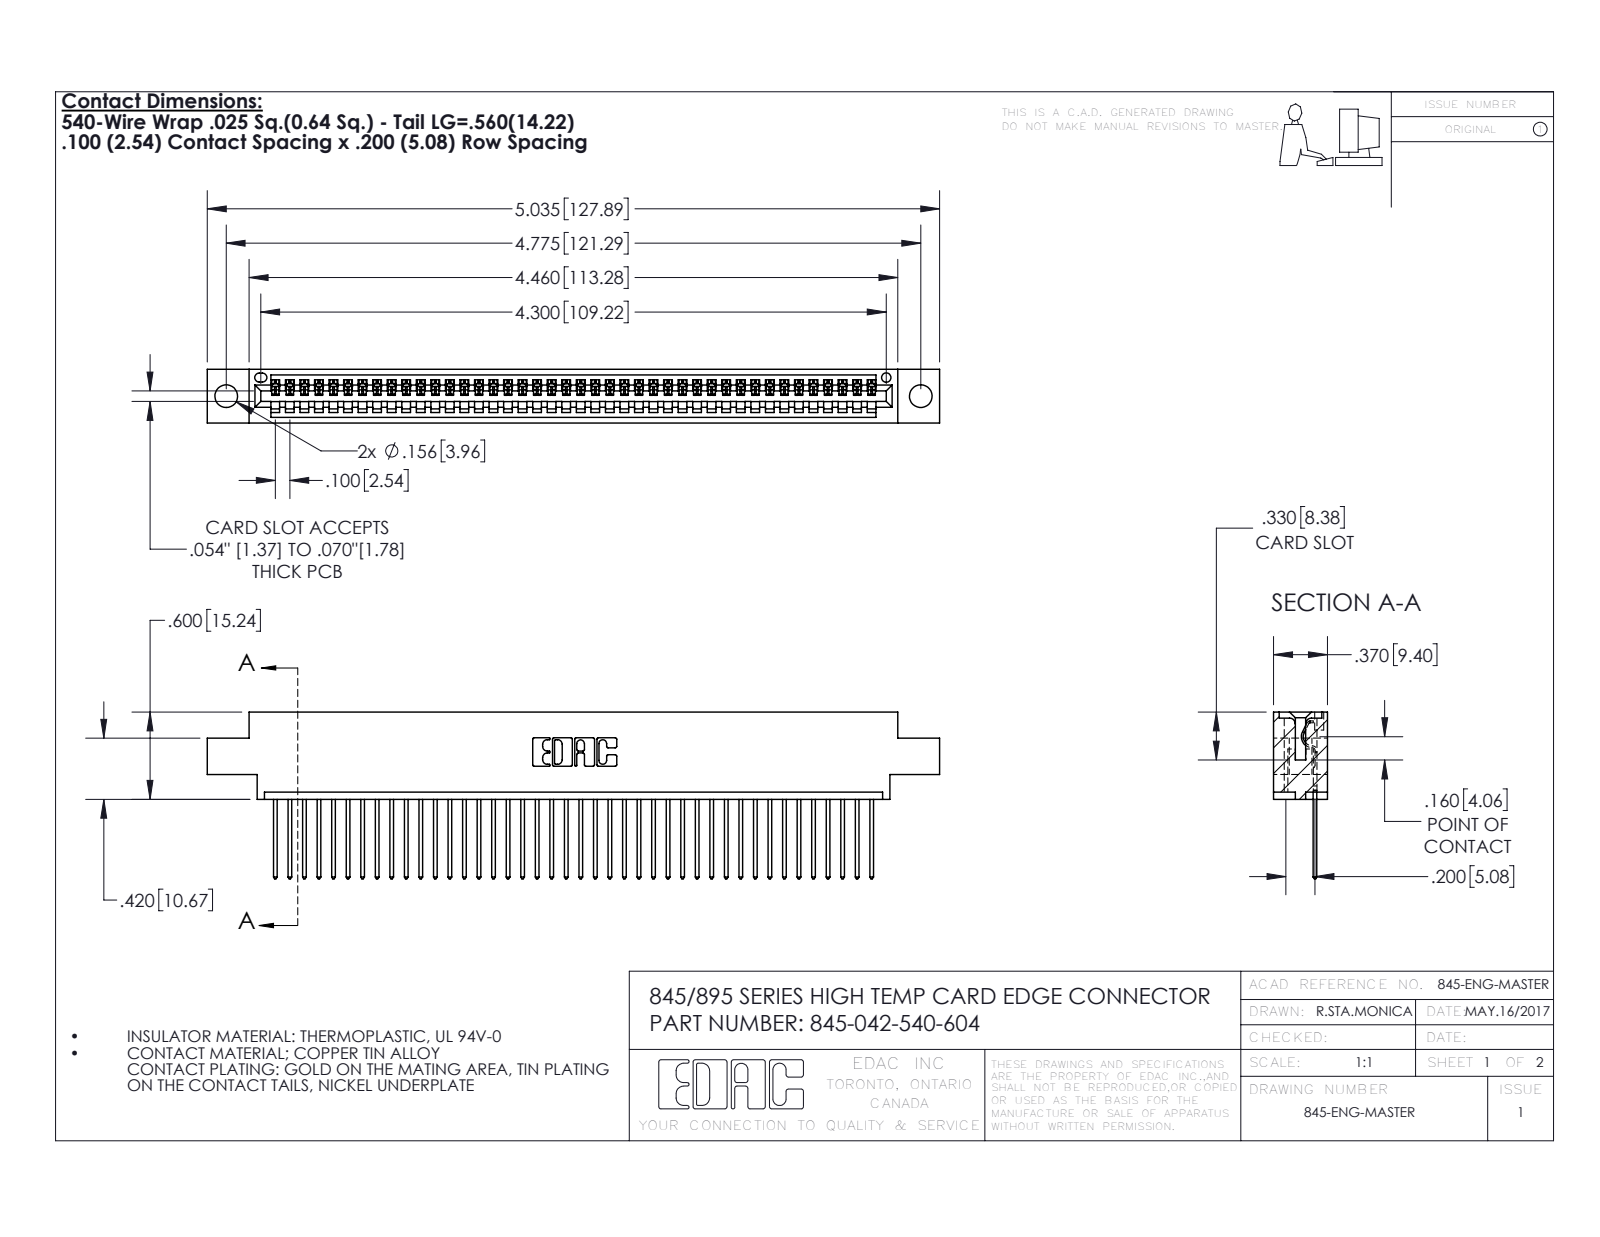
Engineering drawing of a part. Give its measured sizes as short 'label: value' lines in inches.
name: 345-292-001_345-293-140; 345-042-540-604; 345 Part_0.170 Offset - 0.156 Dia-TH
written by: SolidWorks 2016 (CONFIG_CONTROL_DESIGN)
unit: in
bodies: 43 solids, 2566 faces (1764 planar, 802 cylindrical, 0 other)
size: 5.035 × 1.147 × 0.37
volume: 0.732 in³; area: 25.26 in²
holes: 2× ⌀0.156, 1× ⌀0.064
rounds: 84× R0.006, 84× R0.01, 22× R0.01, 6× R0.007, 6× R0.031, 3× R0.026, 2× R0.031, 2× R0.04
face distances: 0.298, 0.072, 0.37, 0.098, 0.272, 0.025, 0.2, 0.225, 0.175, 0.149
hole spacings: 0.27, 4.539, 4.775
